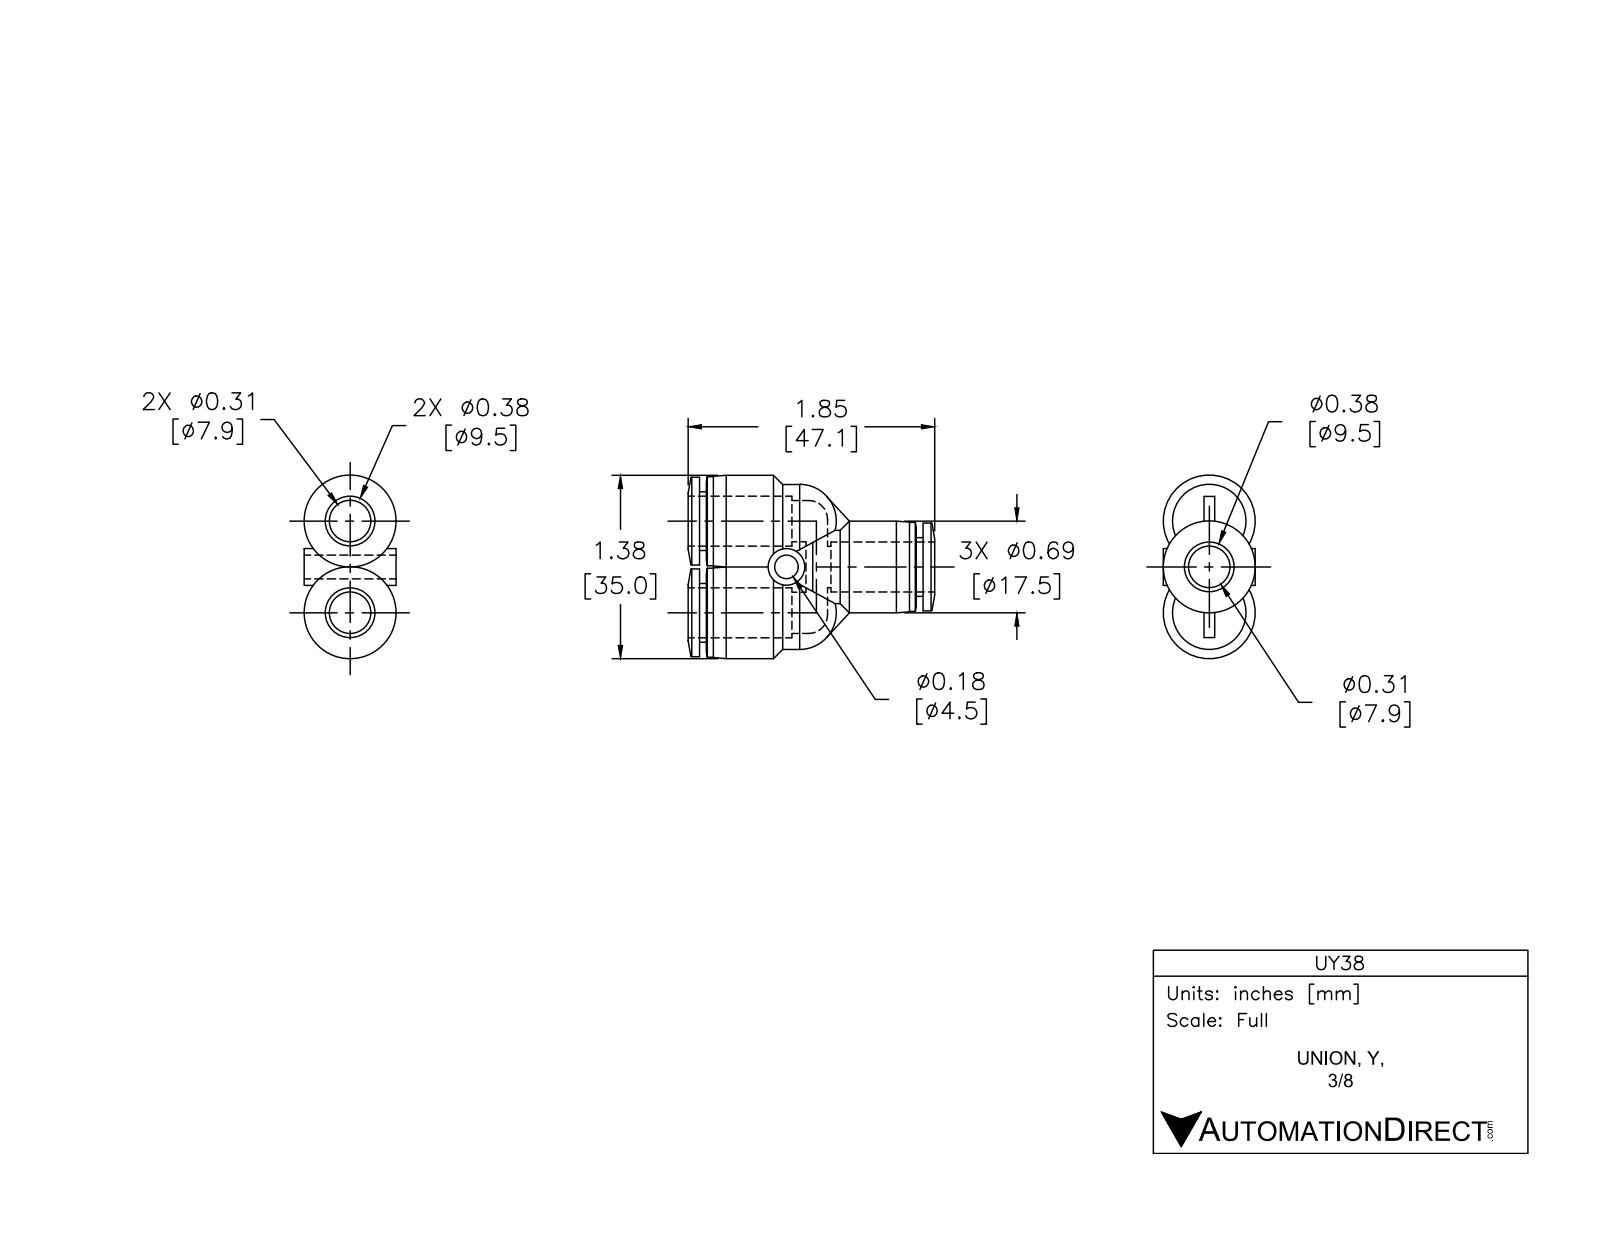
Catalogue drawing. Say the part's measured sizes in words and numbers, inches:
The part is named "UY38". Its 3-D file was written by "SolidWorks 2015 (AUTOMOTIVE_DESIGN)". It is 1 solid with 111 faces: 19 planar, 41 cylindrical and 51 other. Overall it measures 1.854 by 1.378 by 0.689 inches. Its volume is 0.643 cubic inches and its surface area 11.66 square inches. Round holes: 3 of diameter 0.386, 1 of diameter 0.177. Round bosses or shafts: 3 of diameter 0.689, 3 of diameter 0.669, 3 of diameter 0.661, 3 of diameter 0.441, 1 of diameter 0.551, 1 of diameter 0.276. Partial cylindrical surfaces (rounded edges, fillets, slot ends): 2 of radius 0.276. The main face-to-face distances are 0.051, 1.63, 0.693, 0.988, 0.642, 0.937, 1.681, 1.579, 0.295, 0.394. The hole center spacings are 0.344, 0.689.
